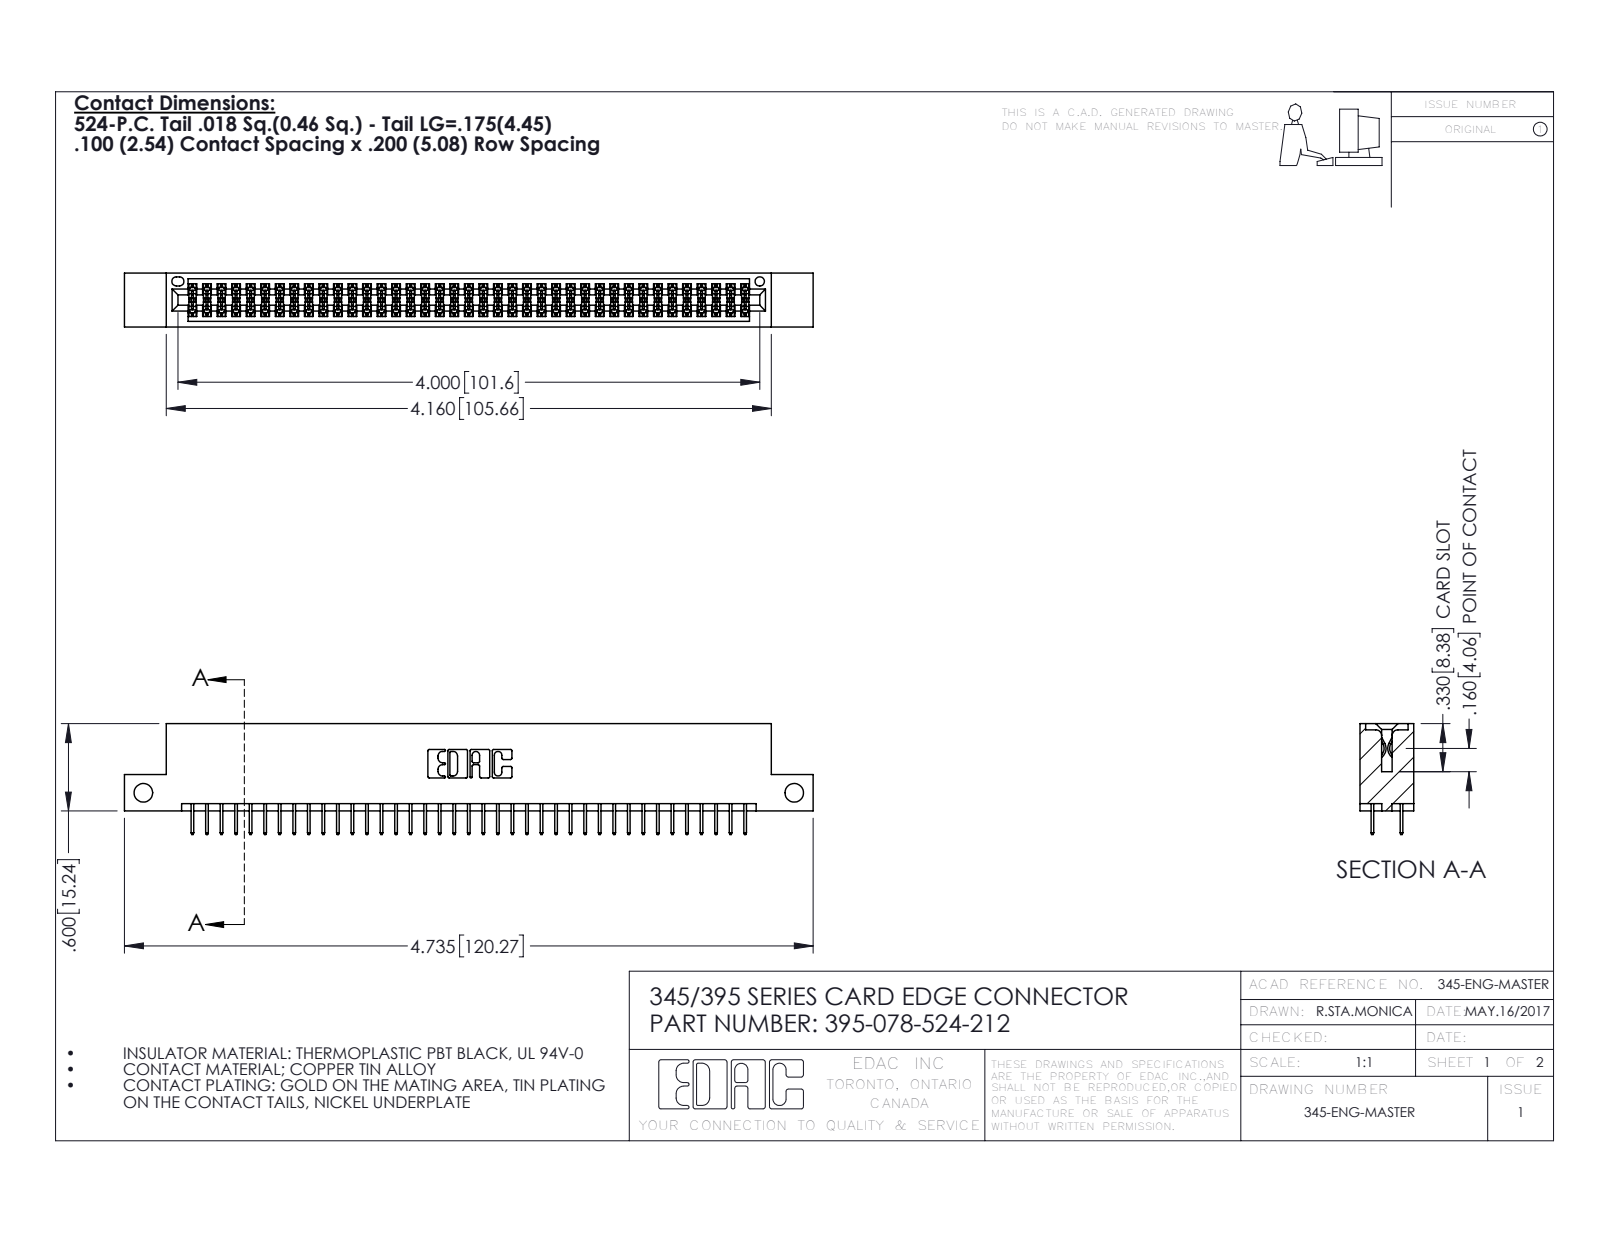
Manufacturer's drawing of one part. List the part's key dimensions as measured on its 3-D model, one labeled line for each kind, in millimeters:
Part name (STEP PRODUCT): 345-292-001_345-293-124; 345 Part_Flush Mounting Lugs - Side Mount; 395-078-524-212
STEP written by: SolidWorks 2016 (CONFIG_CONTROL_DESIGN)
Units: millimetres
Bodies: 79 solids, 4338 faces (3122 planar, 1216 cylindrical, 0 other)
Overall size (bounding box): 120.3 × 19.4 × 9.4
Volume: 11 500 mm³ · Surface area: 16 420 mm²
Round holes (diameter × count): ⌀3.3 ×2, ⌀1.6 ×1
Partial cylindrical surfaces — rounded edges, fillets, slot ends (radius × count): R0.2 ×117, R0.3 ×22, R0.2 ×6, R0.8 ×6, R0.7 ×3, R0.4 ×2, R0.5 ×2, R0.6 ×2
Main face-to-face distances: 7.6, 1.8, 5.1, 9.4, 2.5, 6.9, 0.6, 5.7, 1.8, 4.4
Hole centre spacings: 113.7
